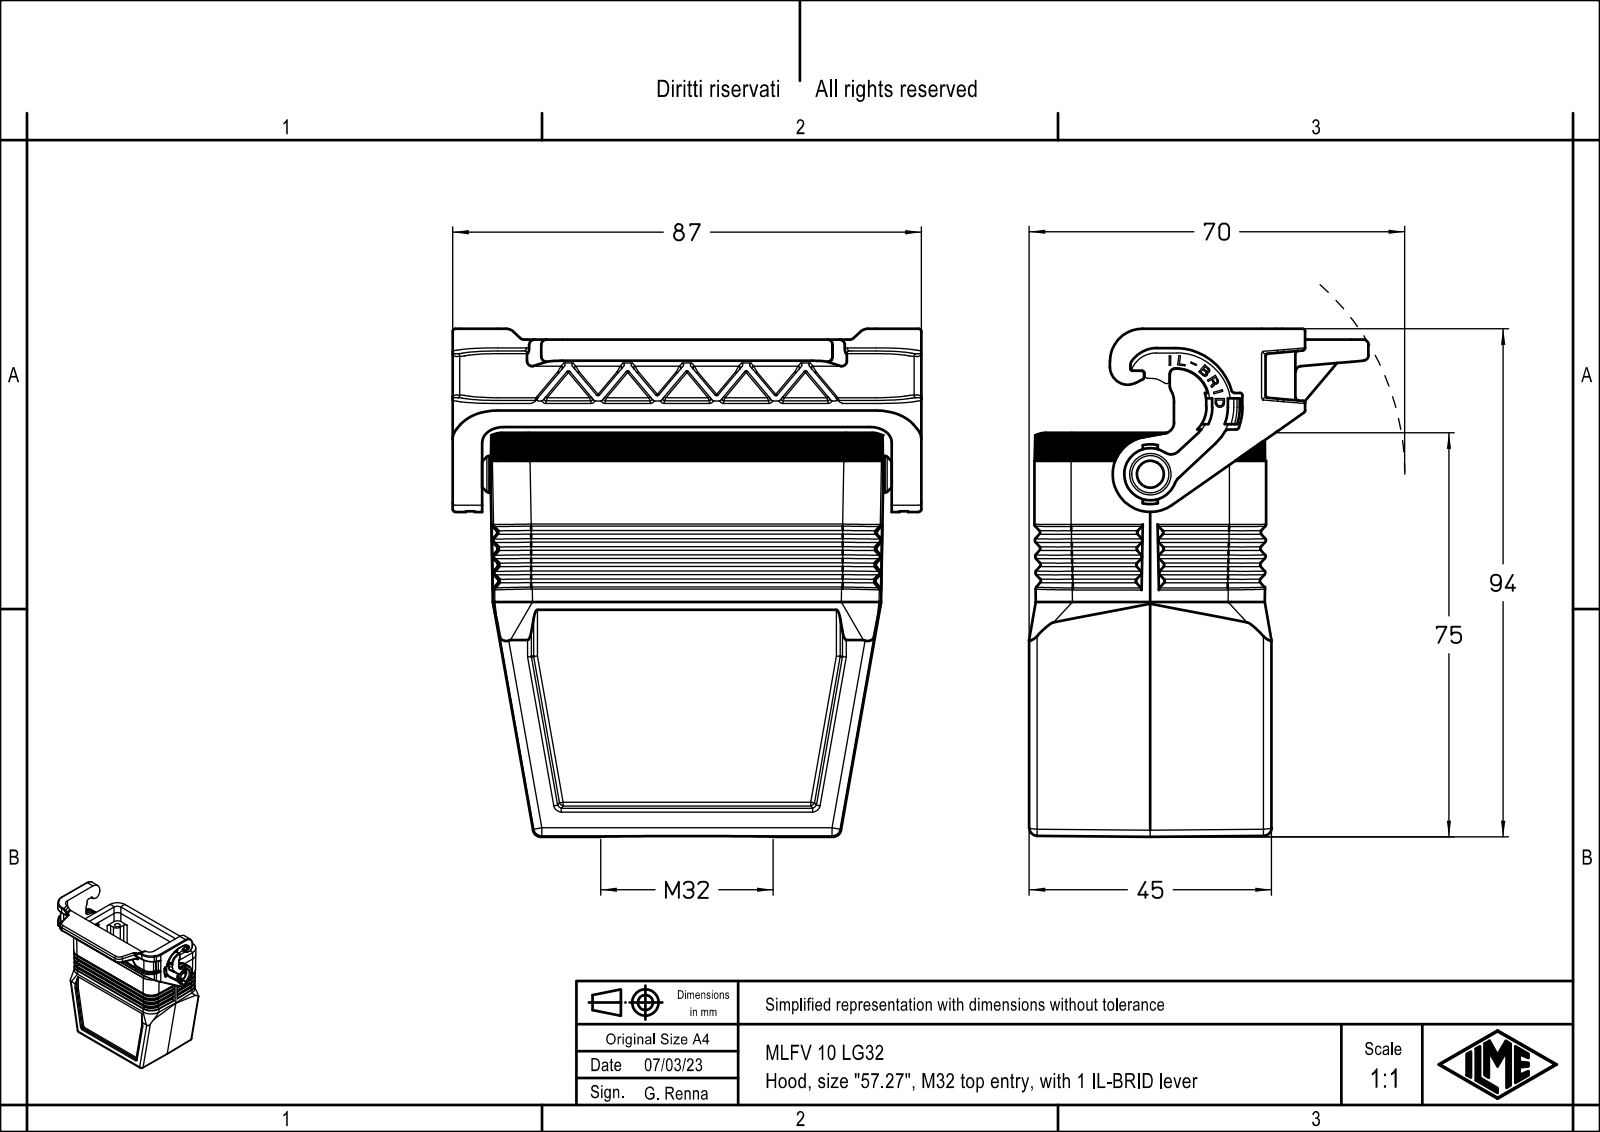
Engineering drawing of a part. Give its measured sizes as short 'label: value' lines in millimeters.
name: MLFV 10 LG32
written by: Creo Elements/Direct Modeling 20.1B 02-Apr-2019 (C) Parametric Technology GmbH (AUTOMOTIVE_DESIGN)
unit: mm
bodies: 1 solid, 1231 faces (708 planar, 303 cylindrical, 220 other)
size: 94.25 × 87 × 63
volume: 86 785 mm³; area: 45 770 mm²
holes: 4× ⌀3, 4× ⌀3.5, 1× ⌀3.25, 1× ⌀5.4, 1× ⌀7.7
bosses: 1× ⌀6.9, 1× ⌀6.8, 1× ⌀5.2, 1× ⌀3.2
rounds: 27× R0.1, 25× R0.5, 25× R1.5, 15× R0.2, 14× R1, 14× R7, 13× R0.33, 12× R3
face distances: 39.25, 3.75, 1, 43, 4.75, 7, 34.5, 38.25, 35.5, 2
hole spacings: 27, 57, 63.07
